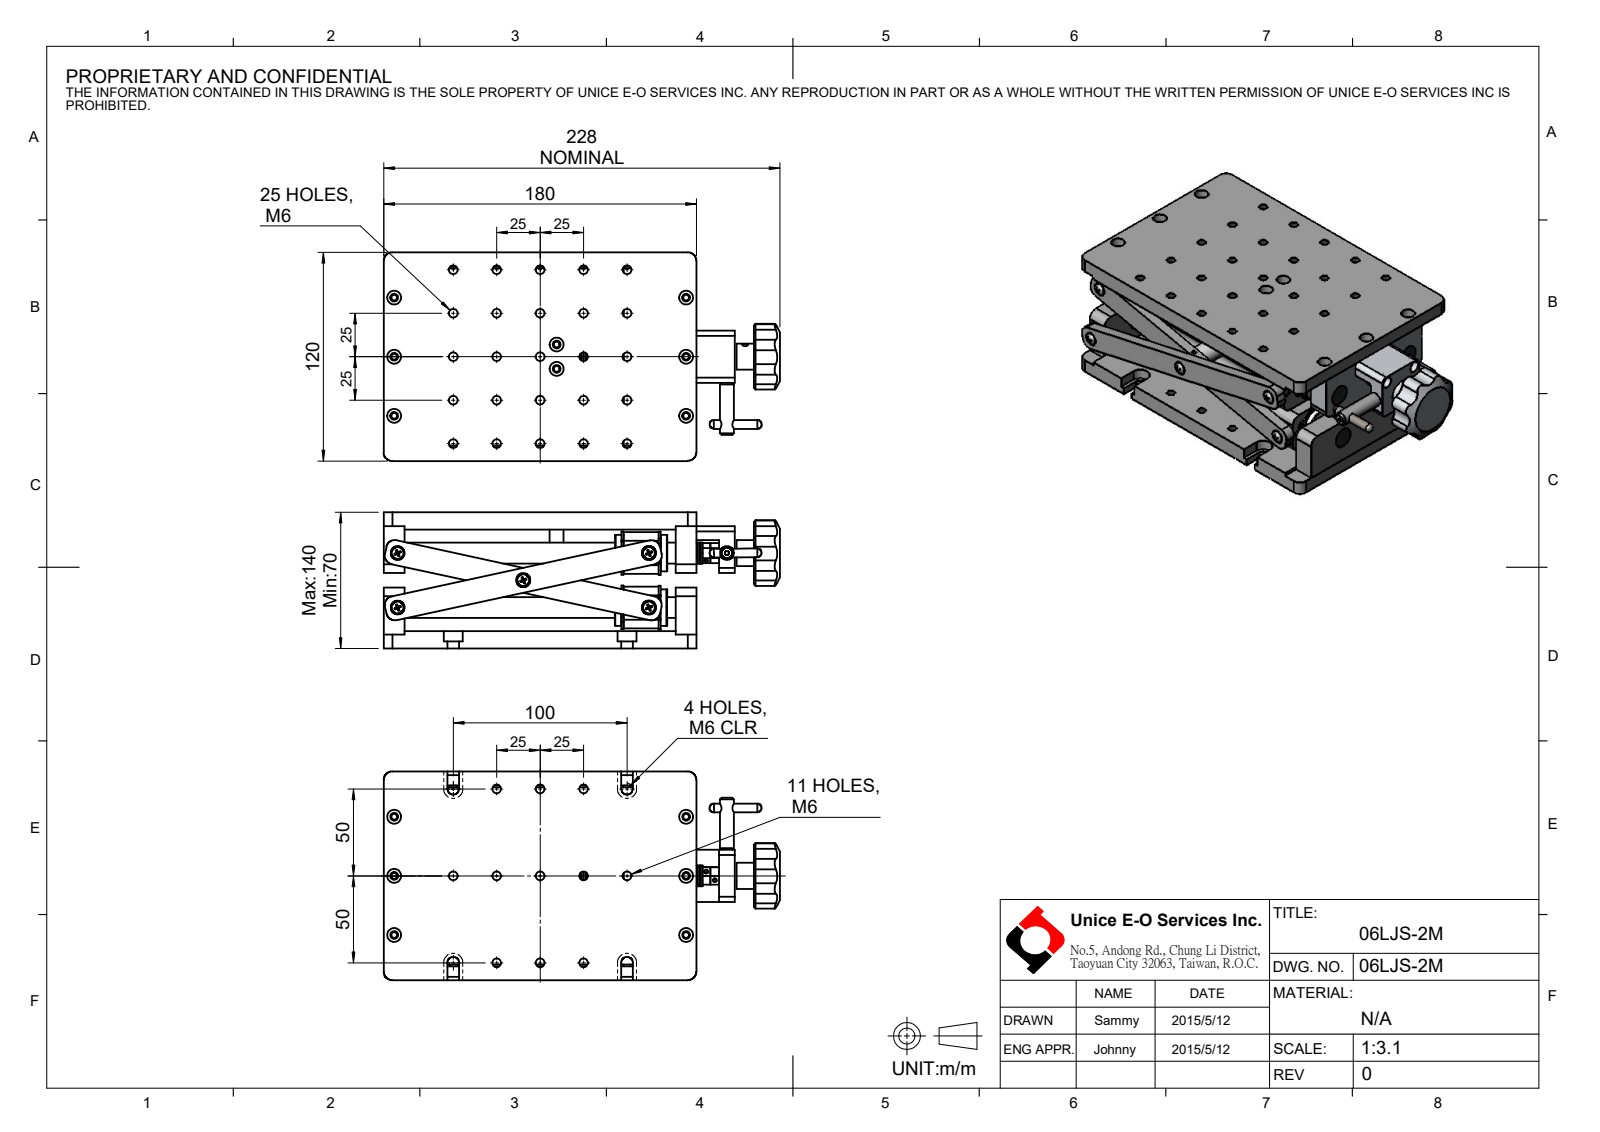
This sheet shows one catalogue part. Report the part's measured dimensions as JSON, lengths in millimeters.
{"part_name": "06LJS-2M", "step_written_by": "SolidWorks 2020 (CONFIG_CONTROL_DESIGN)", "units": "millimeters", "bodies": {"solids": 112, "faces": 2333, "planar": 825, "cylindrical": 947, "other": 561}, "overall_size": [228, 120, 76.24], "volume_mm3": 784417, "surface_area_mm2": 270015, "round_holes": [[5, 33], [2.5, 30], [2.2, 16], [8, 14], [3.3, 9], [4.5, 8], [7, 6], [12, 4], [20, 4], [3.4, 2], [6.5, 2], [5.1, 1]], "round_bosses_or_shafts": [[3, 29], [4, 9], [25, 8], [7, 8], [5.5, 6], [5.6, 5], [21, 4], [12, 2]], "partial_cylinders_radius": [[3, 36], [5, 26], [4, 8], [7.41, 8], [3.3, 4], [5.5, 4]], "face_to_face_distances": [10, 66.24, 76.24, 56.24, 8, 2, 12, 58.24, 68.24, 7], "hole_center_spacings": [55.9, 25, 35.36, 50, 79.06, 90.14, 70.71, 75]}
